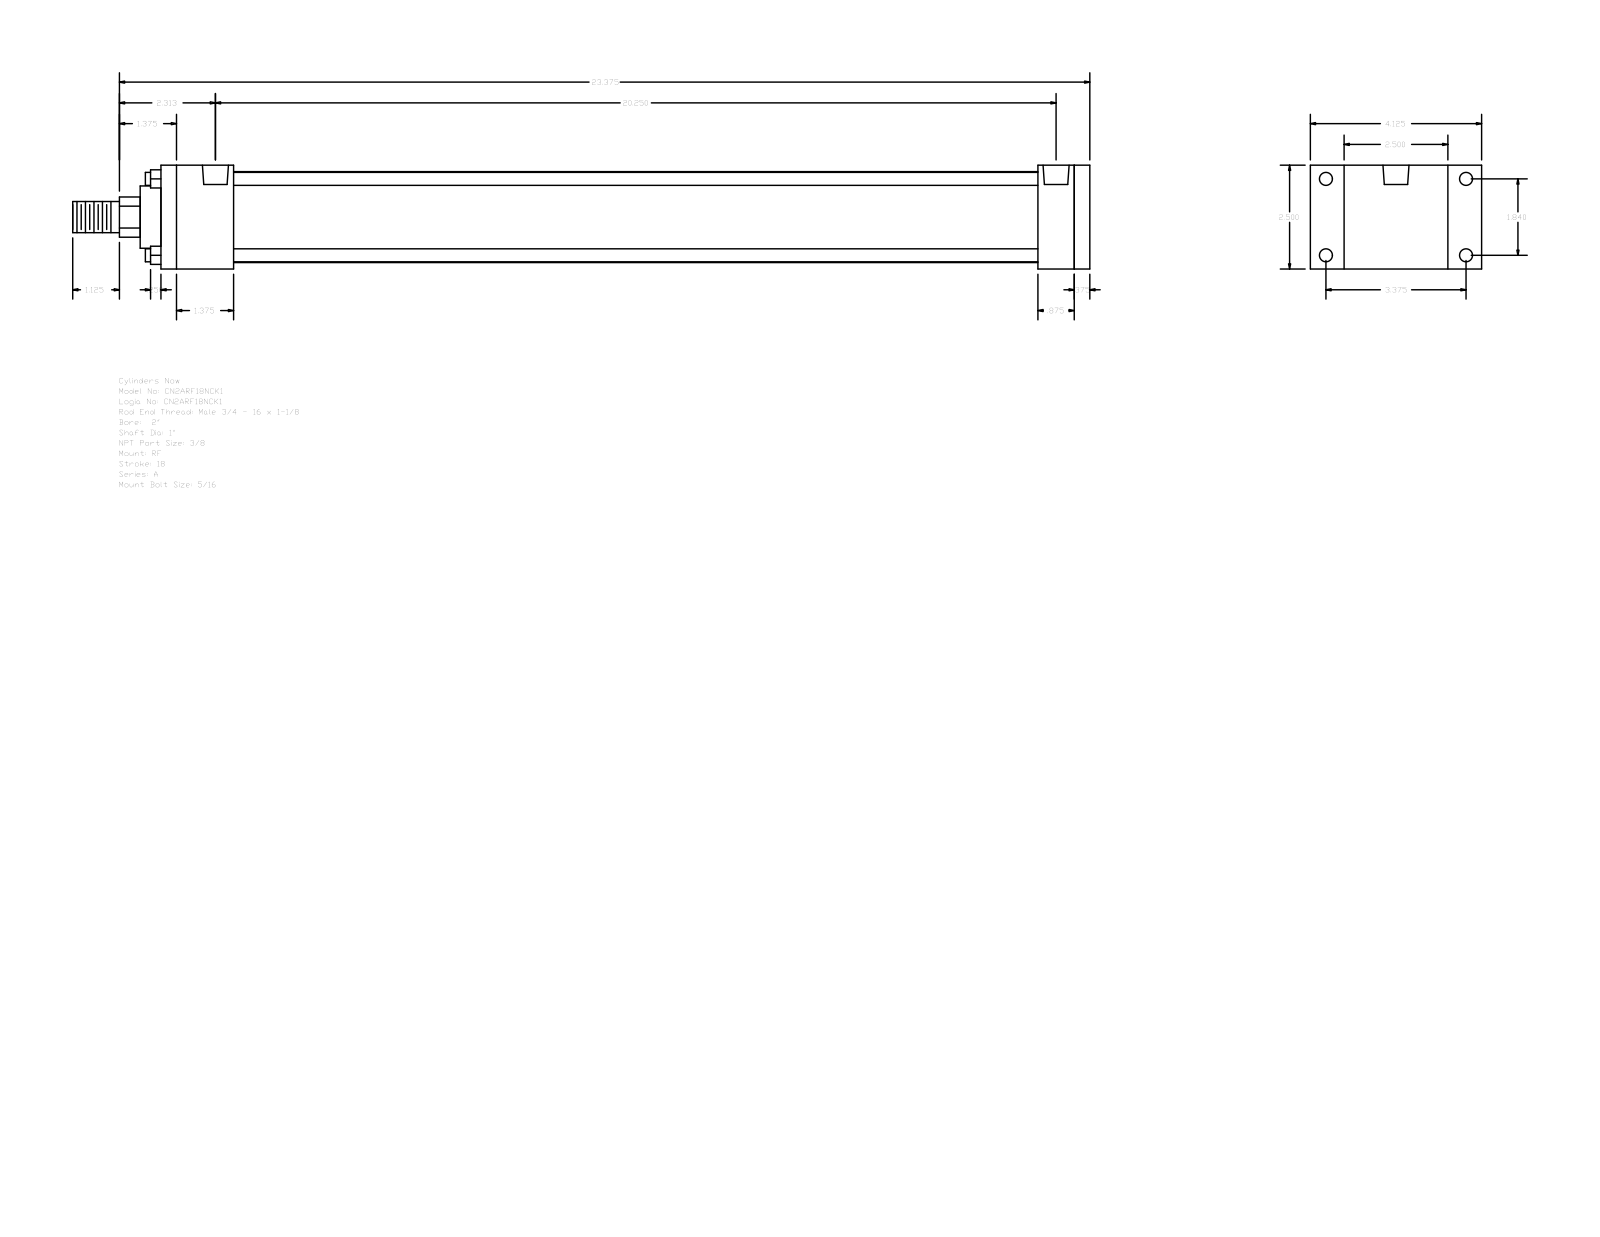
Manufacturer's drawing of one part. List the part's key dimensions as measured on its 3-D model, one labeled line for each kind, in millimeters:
Part name (STEP PRODUCT): A_RF__0200_1
STEP written by: GSSL Pune (CONFIG_CONTROL_DESIGN)
Units: millimetres
Bodies: 0 solids, 92 faces (64 planar, 28 cylindrical, 0 other)
Overall size (bounding box): 622.3 × 104.78 × 63.5
Round holes (diameter × count): ⌀5.56 ×4, ⌀7.94 ×4, ⌀15.93 ×2
Round bosses / shafts (diameter × count): ⌀7.94 ×4, ⌀55.63 ×1, ⌀38.1 ×1, ⌀25.4 ×1, ⌀19.05 ×1
Partial cylindrical surfaces — rounded edges, fillets, slot ends (radius × count): R12.29 ×1
Main face-to-face distances: 63.5, 9.53, 568.33, 558.8, 44.45, 20.64, 514.35, 523.88, 536.58, 492.13
Hole centre spacings: 46.74, 85.72, 97.63, 508.78, 1.59, 3.98, 510.37, 512.76
